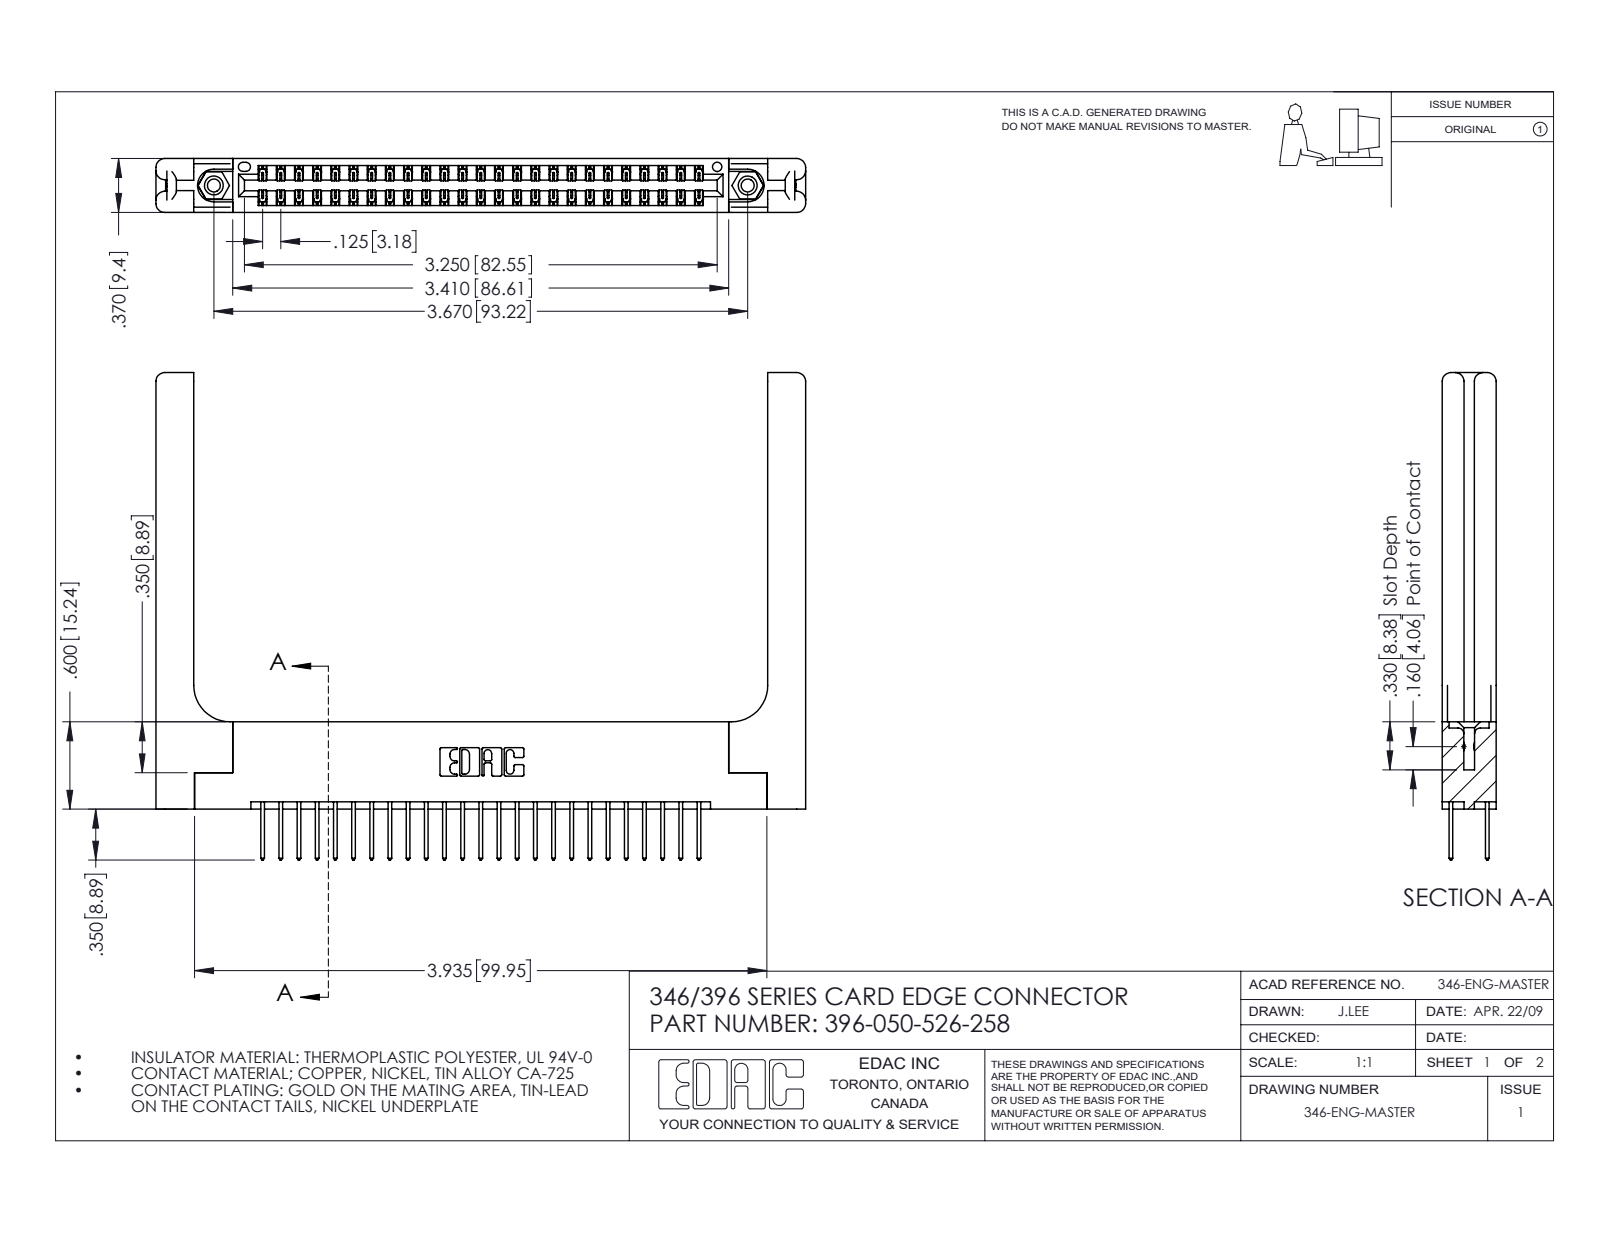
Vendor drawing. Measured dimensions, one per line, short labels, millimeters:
name: 346-220-058_345-220-058; 345-250-001_345-250-001-102; 396-050-526-258; 345-292-001_345-293-126 (+1 more)
written by: SolidWorks 2016 (CONFIG_CONTROL_DESIGN)
unit: mm
bodies: 55 solids, 2978 faces (1974 planar, 944 cylindrical, 60 other)
size: 113.4 × 85.1 × 9.4
volume: 18 500 mm³; area: 20 210 mm²
holes: 2× ⌀2.3, 2× ⌀3.2, 2× ⌀4, 1× ⌀1.6
bosses: 2× ⌀3.9
rounds: 75× R0.2, 50× R0.3, 22× R0.3, 16× R1.5, 6× R0.2, 6× R0.8, 3× R0.7, 2× R0.4
face distances: 9.4, 1.8, 1.2, 8.2, 6.4, 3.8, 3.8, 0.6, 7.6, 7
hole spacings: 6.2, 87.9, 93.2
